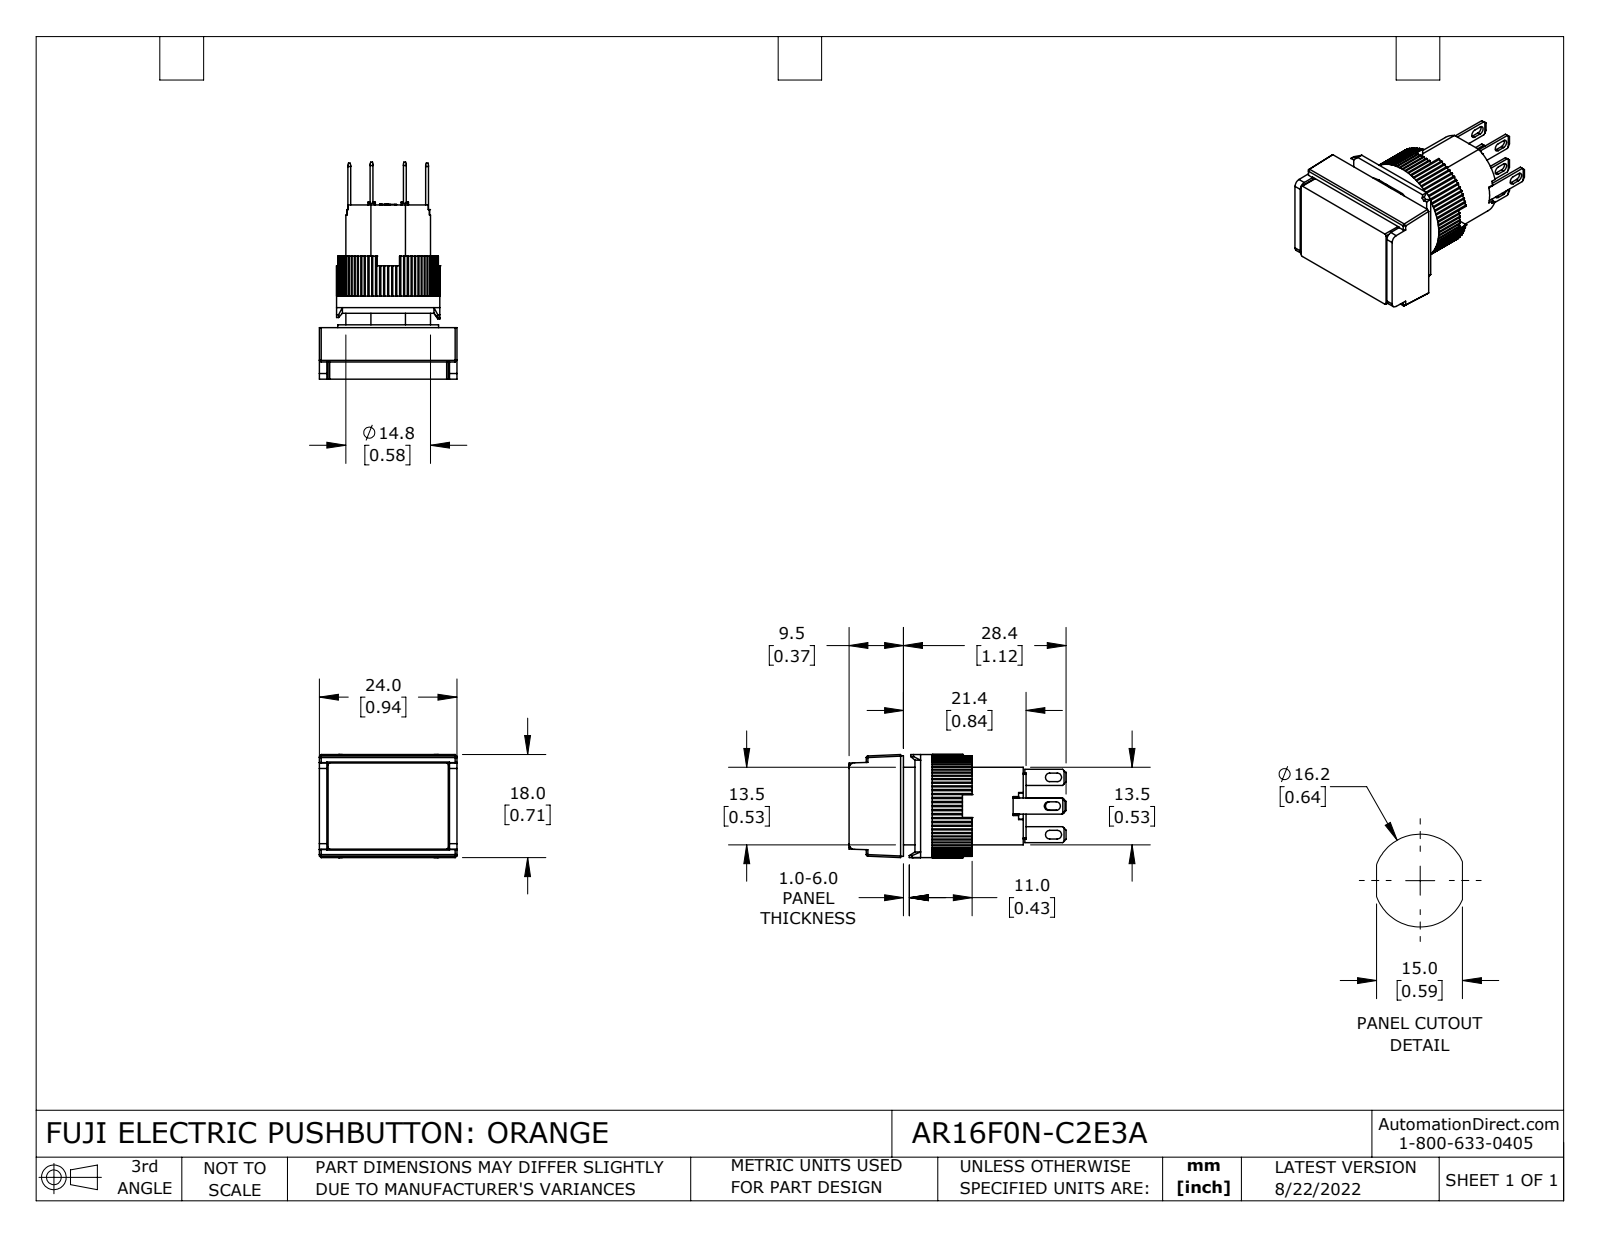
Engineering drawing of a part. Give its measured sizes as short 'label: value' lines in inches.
name: AR16F0N-C2E3A
written by: SolidWorks 2023 (CONFIG_CONTROL_DESIGN)
unit: in
bodies: 14 solids, 845 faces (656 planar, 185 cylindrical, 4 other)
size: 1.492 × 0.945 × 0.709
volume: 0.469 in³; area: 9.459 in²
holes: 1× ⌀0.543, 1× ⌀0.583
bosses: 1× ⌀0.709, 1× ⌀0.693
rounds: 80× R0.01, 12× R0.008, 8× R0.03, 6× R0.012, 2× R0.039, 1× R0.315
face distances: 0.213, 0.354, 0.142, 0.35, 0.492, 0.705, 0.138, 0.02, 0.843, 0.764
